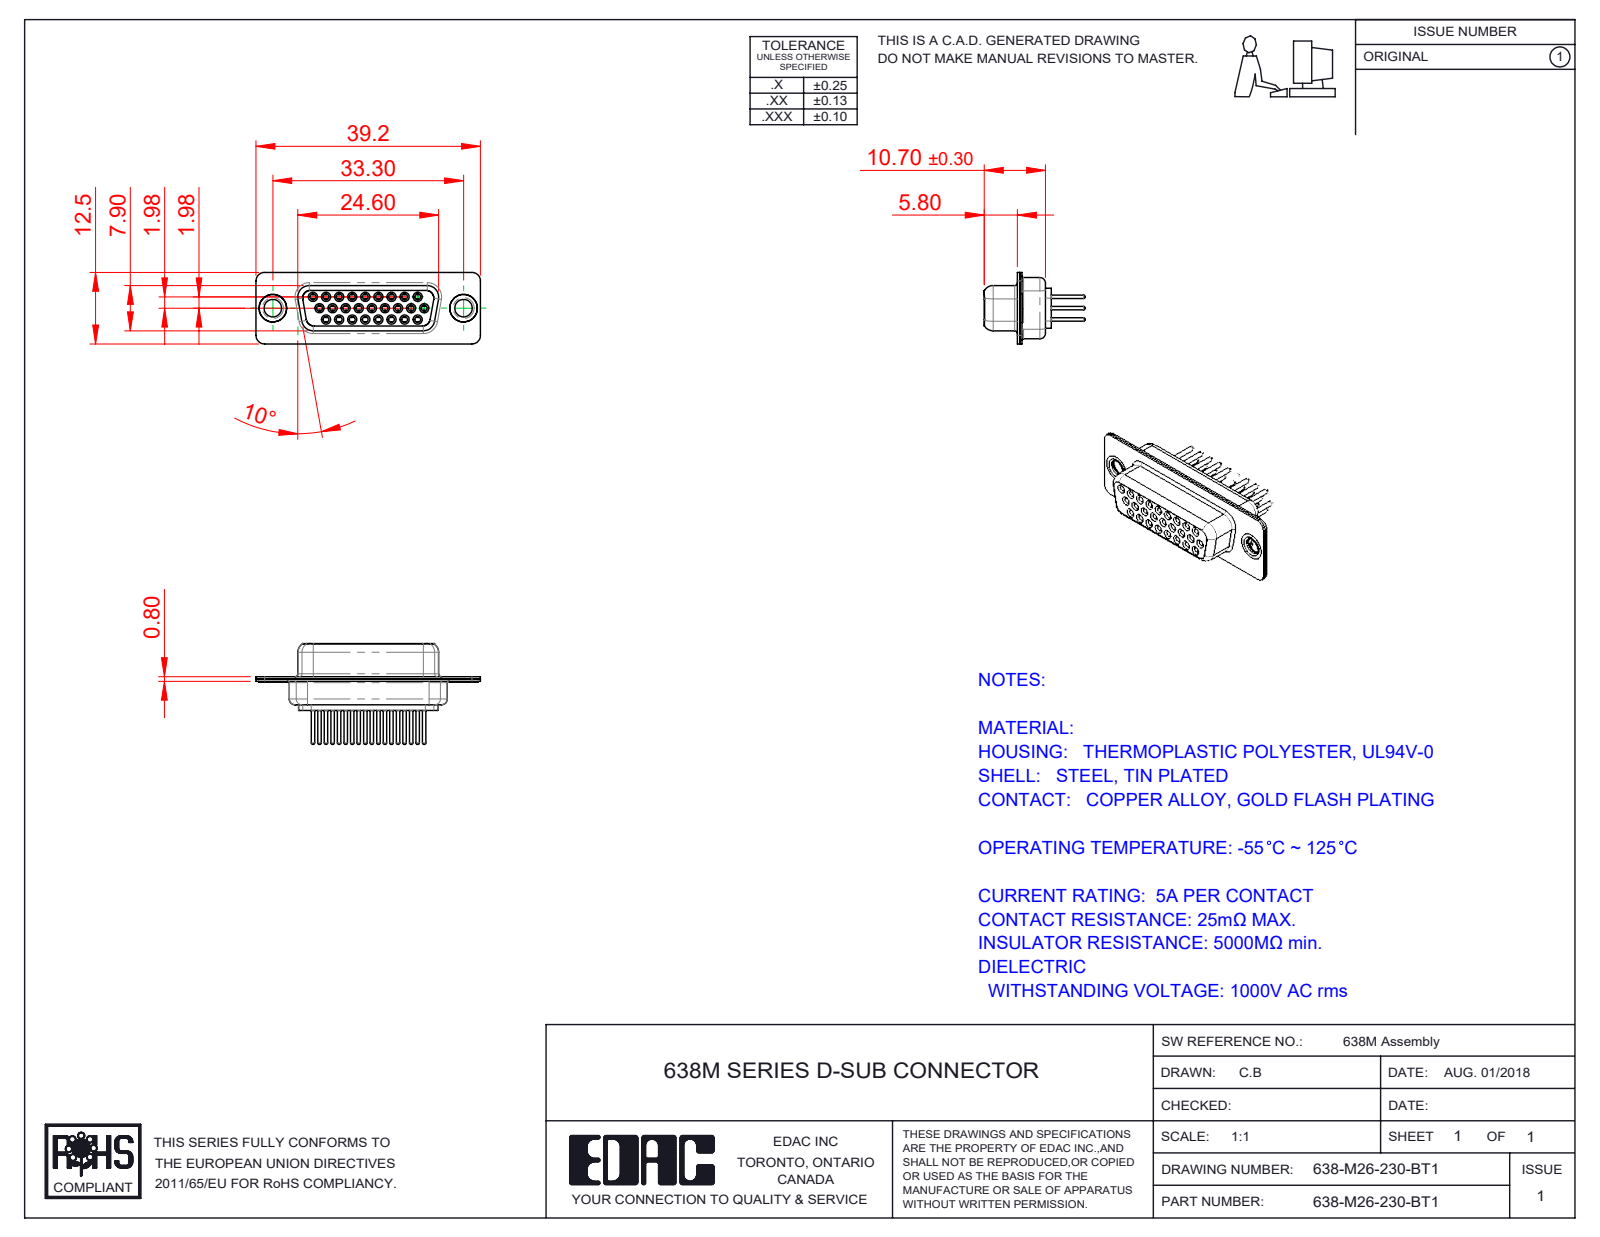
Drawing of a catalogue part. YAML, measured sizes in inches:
part_name: "638M Shell Front_26 Contacts; 638M Housing_26 Contacts; 638M Shell Rear_26 Contacts; 638M Contact Row 1_30 (+4 more)"
step_written_by: "SolidWorks 2020 (CONFIG_CONTROL_DESIGN)"
units: inches
bodies: {solids: 31, faces: 1683, planar: 457, cylindrical: 615, other: 611}
overall_size: [1.543, 0.693, 0.492]
volume: 0.139
surface_area: 11.96
round_holes:
  - {diameter: 0.039, count: 26}
  - {diameter: 0.043, count: 26}
  - {diameter: 0.067, count: 26}
  - {diameter: 0.071, count: 26}
  - {diameter: 0.079, count: 26}
  - {diameter: 0.12, count: 2}
  - {diameter: 0.157, count: 2}
  - {diameter: 0.189, count: 2}
round_bosses_or_shafts:
  - {diameter: 0.087, count: 26}
  - {diameter: 0.063, count: 26}
  - {diameter: 0.059, count: 26}
  - {diameter: 0.024, count: 26}
  - {diameter: 0.197, count: 2}
  - {diameter: 0.193, count: 2}
  - {diameter: 0.14, count: 2}
partial_cylinders:
  - {radius: 0.059, count: 16}
  - {radius: 0.079, count: 12}
  - {radius: 0.053, count: 8}
  - {radius: 0.063, count: 8}
  - {radius: 0.01, count: 4}
  - {radius: 0.02, count: 4}
  - {radius: 0.024, count: 4}
  - {radius: 0.026, count: 4}
face_to_face_distances: [0.016, 0.055, 0.018, 0.333, 0.35, 0.071, 0.039, 0.244, 0.278, 0.053]
hole_center_spacings: [0.156, 0.09, 0.18, 0.238, 0.09, 0.324, 0.27, 0.238]
